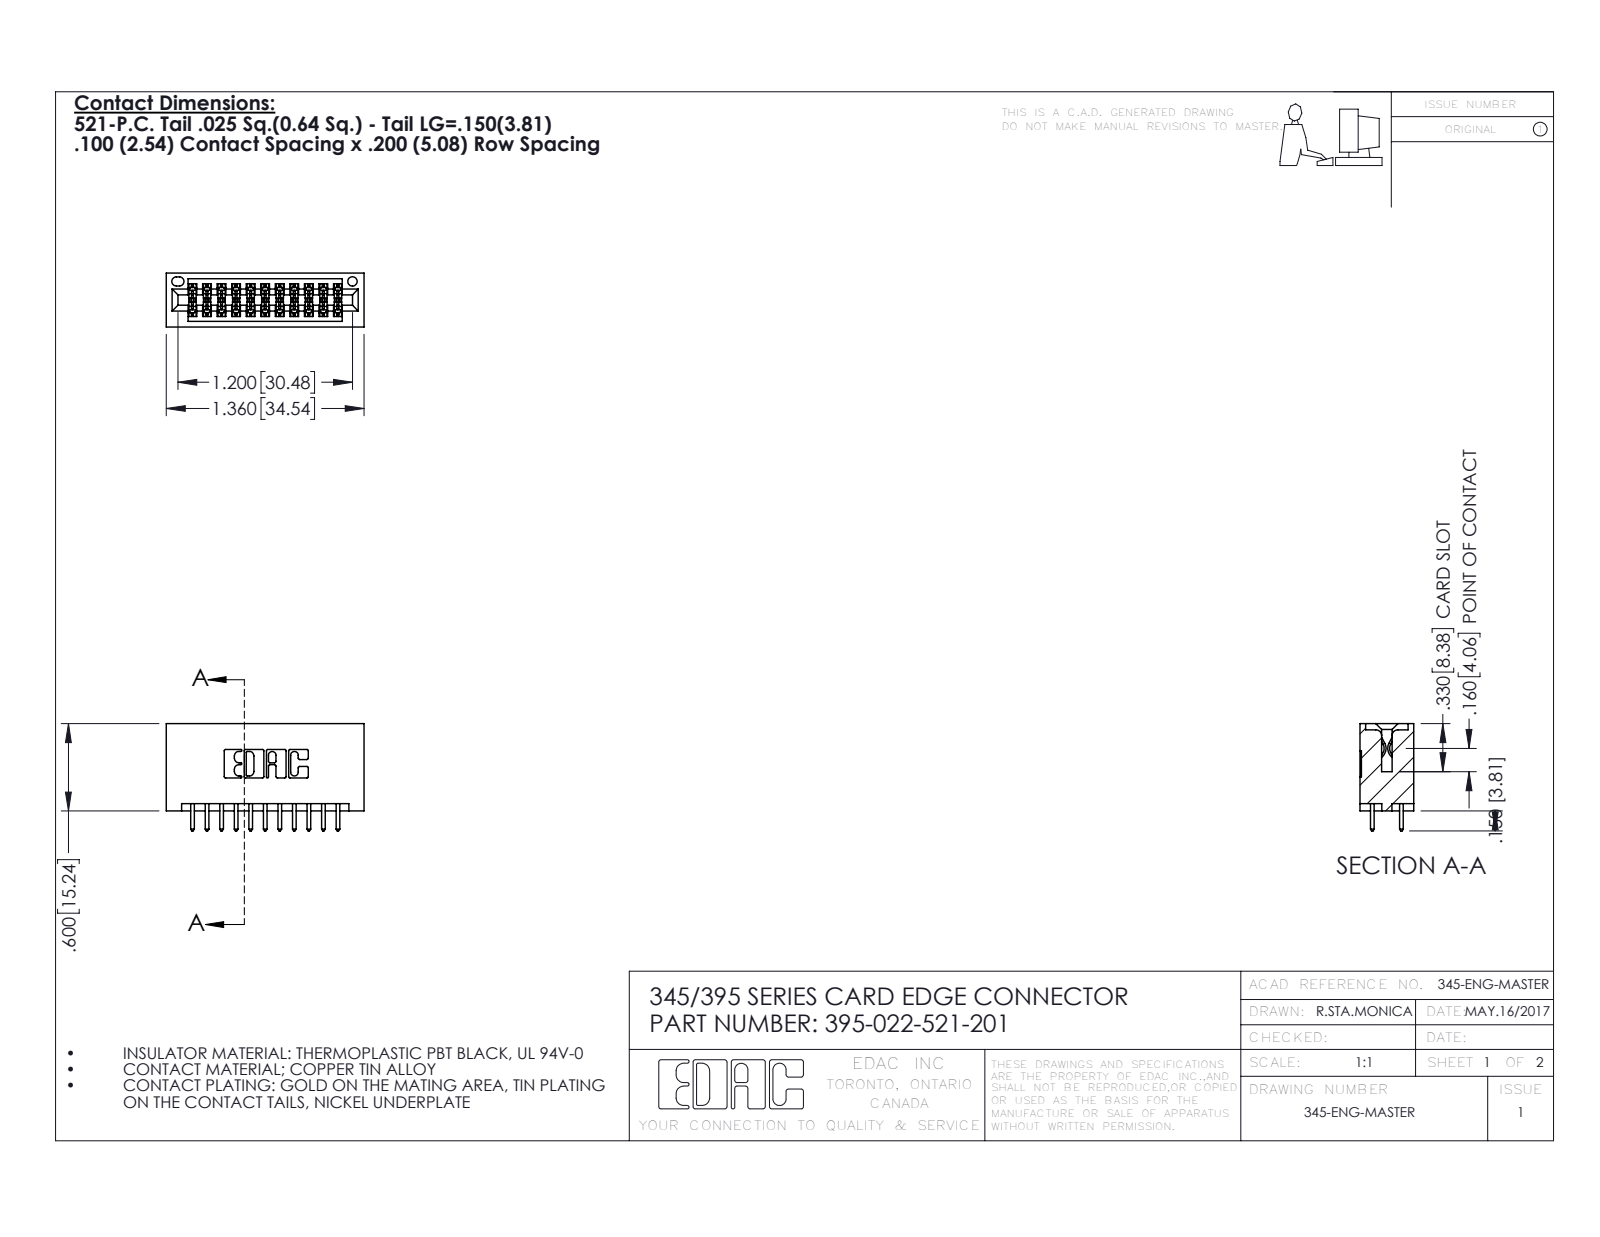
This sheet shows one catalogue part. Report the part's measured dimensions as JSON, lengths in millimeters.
{"part_name": "395-022-521-201; 345 Part_No Mounting Lugs; 345-292-001_345-293-121", "step_written_by": "SolidWorks 2016 (CONFIG_CONTROL_DESIGN)", "units": "millimeters", "bodies": {"solids": 23, "faces": 1218, "planar": 802, "cylindrical": 416, "other": 0}, "overall_size": [34.5, 18.7, 9.4], "volume_mm3": 3670, "surface_area_mm2": 5076, "round_holes": [[1.6, 1]], "partial_cylinders_radius": [[0.2, 33], [0.3, 22], [0.3, 22], [0.2, 6], [0.8, 6], [0.7, 3], [0.4, 2], [0.5, 2]], "face_to_face_distances": [5.1, 7.6, 1.8, 9.4, 2.5, 2.5, 6.9, 0.6, 5.7, 15.2]}
